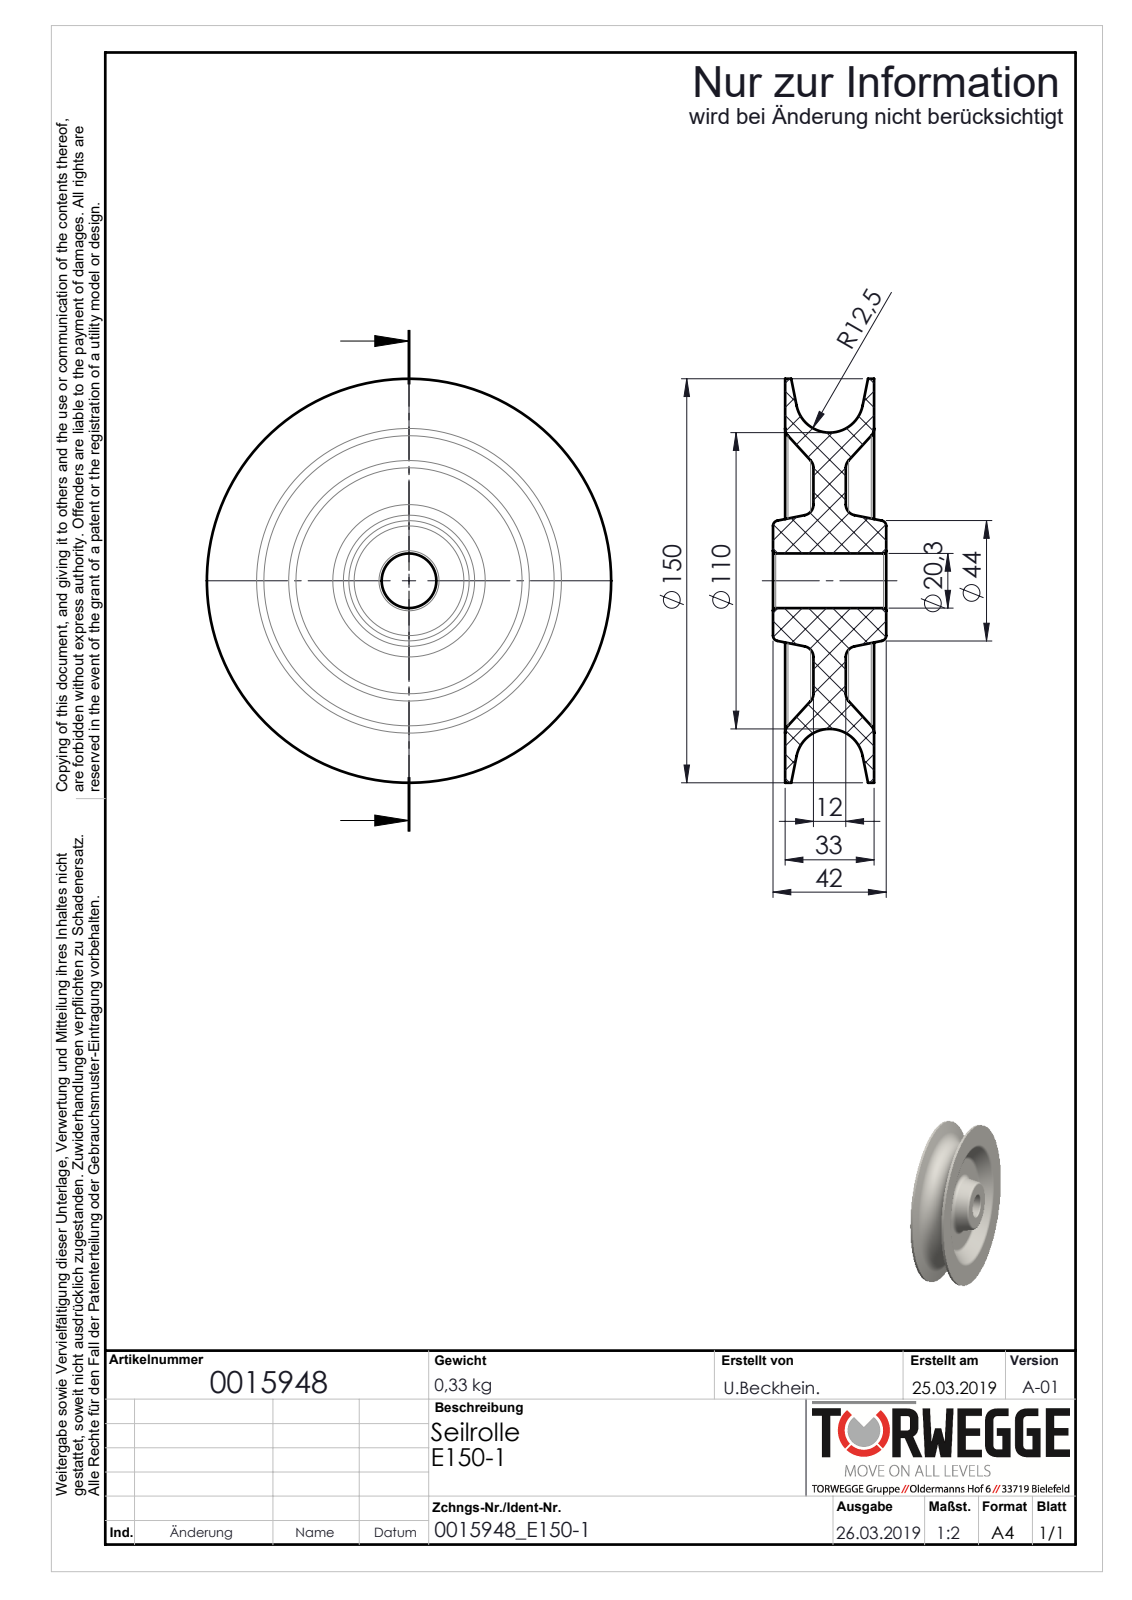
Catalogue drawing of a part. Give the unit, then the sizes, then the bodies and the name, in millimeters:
Units: millimetres
Overall size (bounding box): 150 × 150 × 42
Round holes (diameter × count): ⌀20.3 ×1
Round bosses / shafts (diameter × count): ⌀150 ×1
Main face-to-face distances: 33, 10.5, 22.5, 12, 4.5, 15, 27, 37.5, 42
Volume: 274 593 mm³ · Surface area: 66 511 mm²
Bodies: 1 solid, 48 faces (6 planar, 6 cylindrical, 36 other)
Part name (STEP PRODUCT): 0015948_E150-1_(A-01)
STEP written by: SolidWorks 2018 (AUTOMOTIVE_DESIGN)
